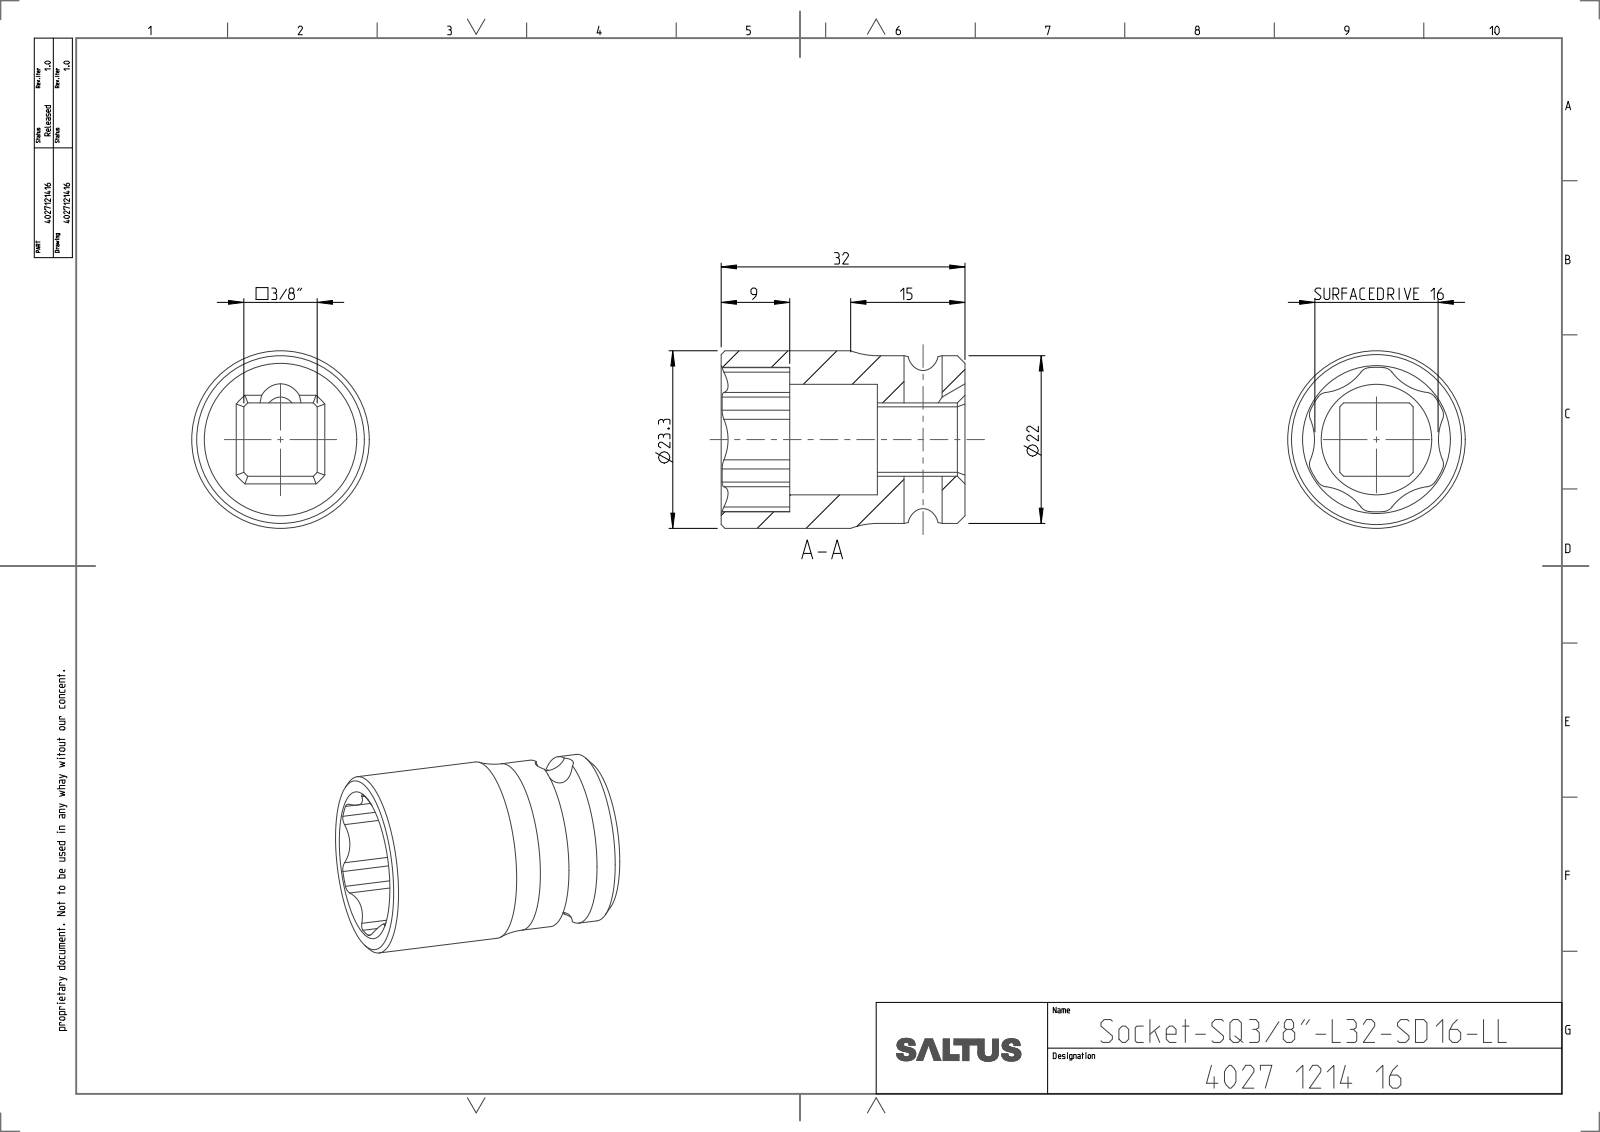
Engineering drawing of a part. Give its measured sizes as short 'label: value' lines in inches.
name: 4027121416
written by: CREO PARAMETRIC BY PTC INC, 2022414 (CONFIG_CONTROL_DESIGN)
unit: in
bodies: 1 solid, 68 faces (13 planar, 41 cylindrical, 14 other)
size: 1.26 × 0.917 × 0.917
volume: 0.441 in³; area: 6.888 in²
holes: 1× ⌀0.197, 1× ⌀0.571
bosses: 1× ⌀0.917, 1× ⌀0.866
rounds: 12× R0.059, 6× R0.268, 1× R0.118, 1× R0.254, 1× R0.373
face distances: 0.379, 0.453, 1.26, 0.906, 0.354, 0.807
